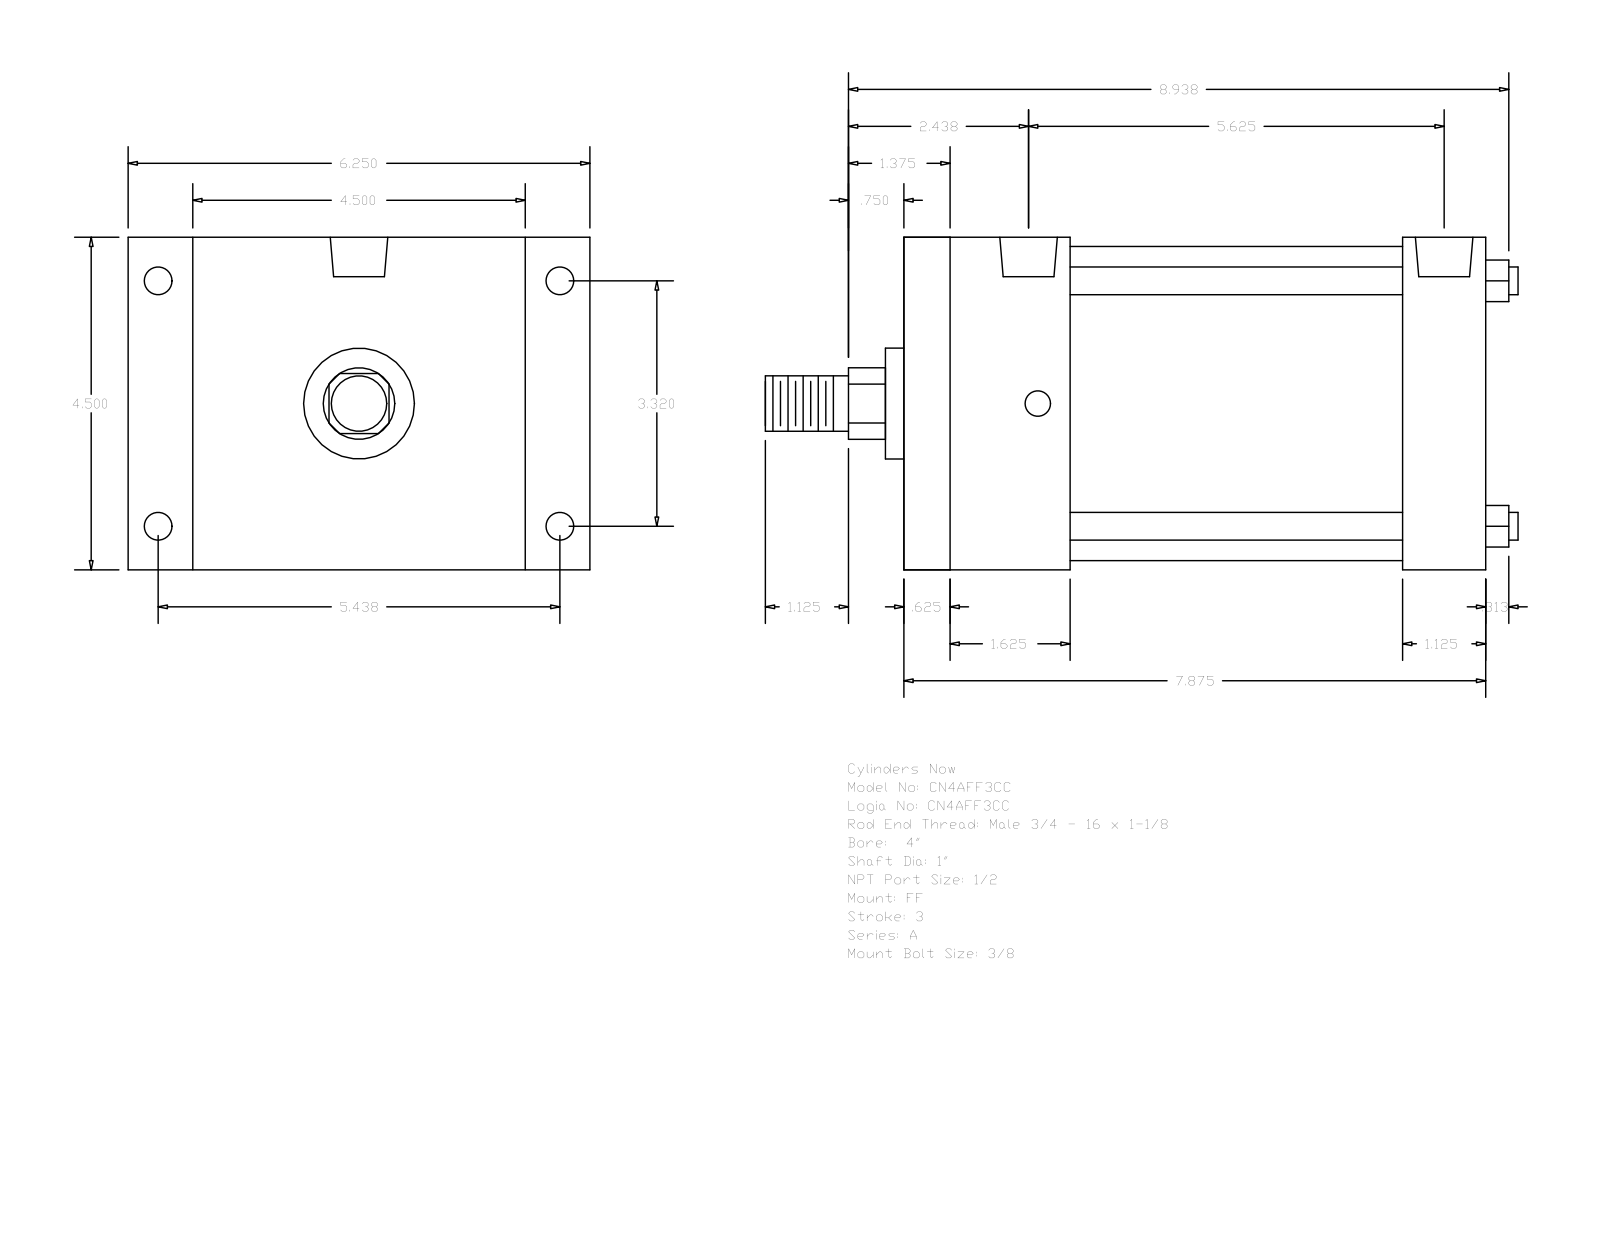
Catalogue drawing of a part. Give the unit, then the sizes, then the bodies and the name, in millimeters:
Units: millimetres
Overall size (bounding box): 258.76 × 158.75 × 114.3
Round holes (diameter × count): ⌀8.73 ×4, ⌀9.53 ×4, ⌀19.77 ×2
Round bosses / shafts (diameter × count): ⌀9.53 ×4, ⌀107.95 ×1, ⌀38.1 ×1, ⌀25.4 ×1, ⌀19.05 ×1
Partial cylindrical surfaces — rounded edges, fillets, slot ends (radius × count): R12.29 ×1
Main face-to-face distances: 114.3, 200.02, 15.87, 184.15, 28.57, 22.23, 136.53, 171.45, 155.58, 57.15
Hole centre spacings: 3.18, 84.32, 136.52, 138.12, 139.7, 161.82, 142.88
Bodies: 0 solids, 92 faces (64 planar, 28 cylindrical, 0 other)
Part name (STEP PRODUCT): A_FF__0400_1
STEP written by: GSSL Pune (CONFIG_CONTROL_DESIGN)
